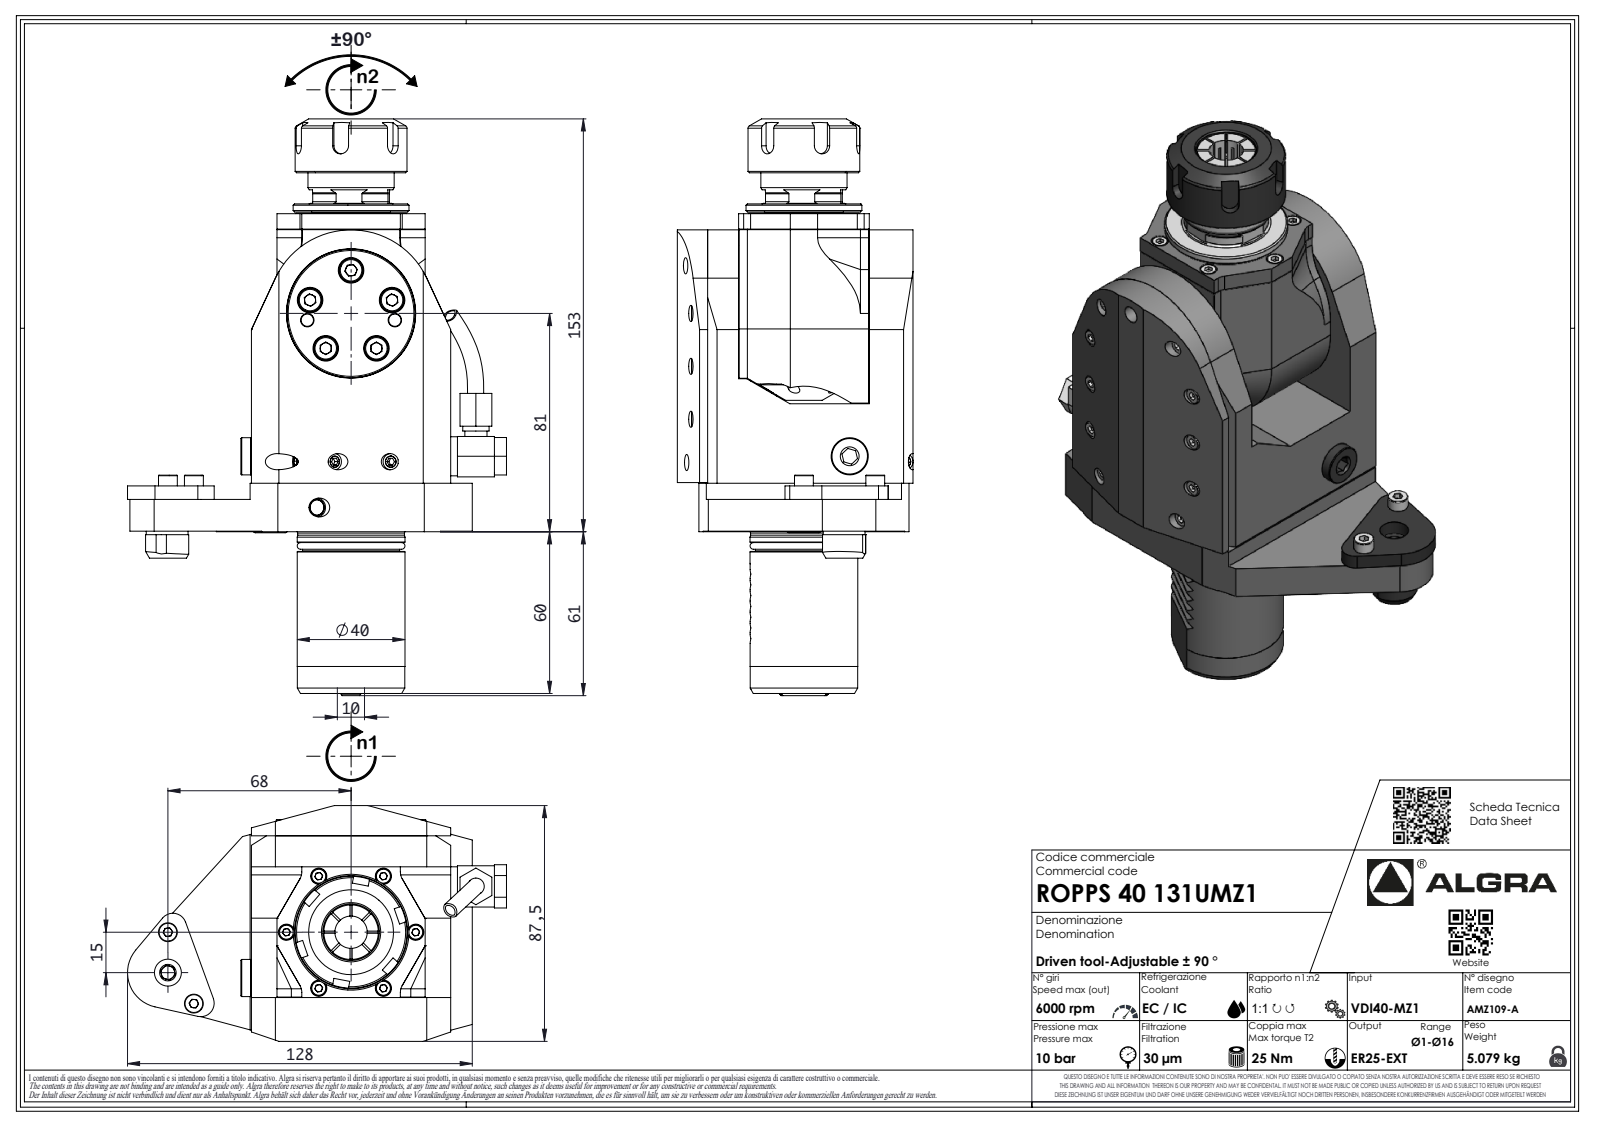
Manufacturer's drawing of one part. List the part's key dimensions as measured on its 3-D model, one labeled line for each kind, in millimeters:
Part name (STEP PRODUCT): ROPPS40131UMZ1
STEP written by: SolidWorks 2023 (AUTOMOTIVE_DESIGN)
Units: millimetres
Bodies: 1 solid, 626 faces (413 planar, 97 cylindrical, 116 other)
Overall size (bounding box): 214.39 × 140.7 × 87.5
Volume: 738 734 mm³ · Surface area: 78 658 mm²
Round holes (diameter × count): ⌀2.1 ×1
Round bosses / shafts (diameter × count): ⌀7 ×2, ⌀43 ×1, ⌀41.5 ×1, ⌀41 ×1, ⌀40 ×1, ⌀39.9 ×1, ⌀39.6 ×1, ⌀36 ×1
Partial cylindrical surfaces — rounded edges, fillets, slot ends (radius × count): R0.33 ×7, R0.52 ×7, R1.75 ×7, R3.7 ×7, R3 ×6, R5.1 ×4, R5 ×2, R20 ×2
Main face-to-face distances: 74, 8, 47.5, 14.75, 63.25, 78, 64.75, 55, 60, 118.4
